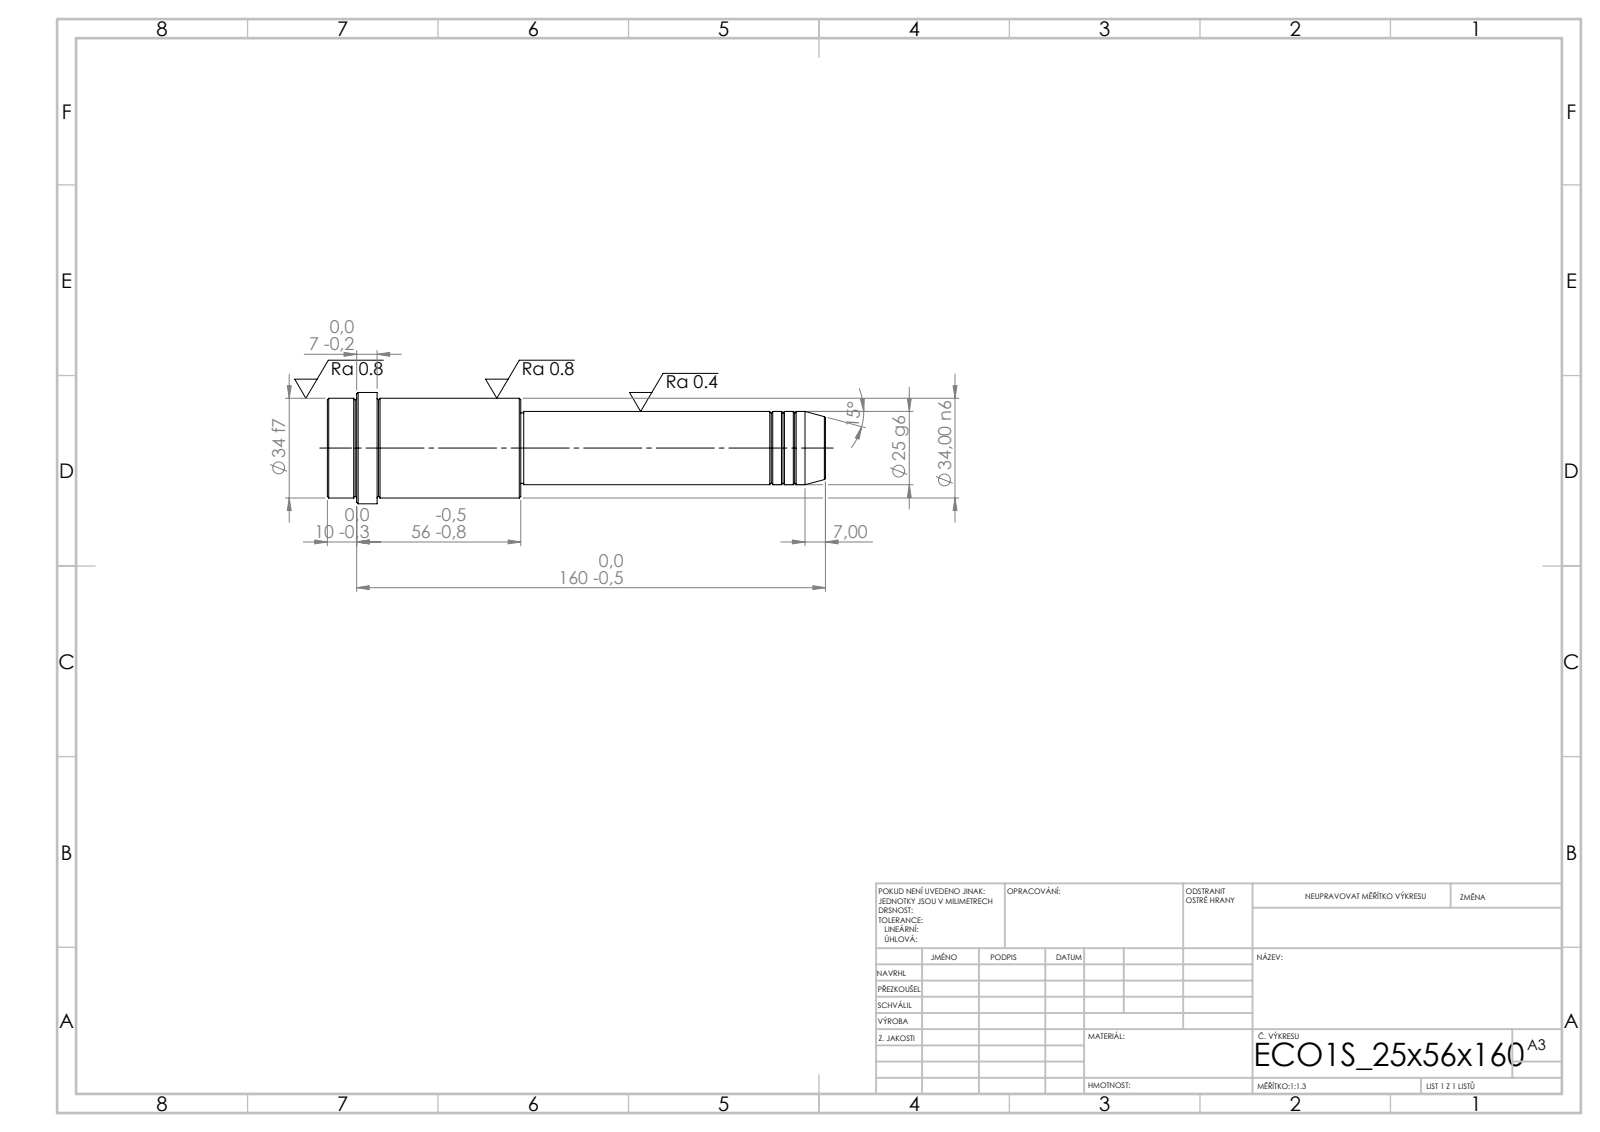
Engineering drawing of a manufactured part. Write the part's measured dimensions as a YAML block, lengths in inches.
step_written_by: "SolidWorks 2019 (CONFIG_CONTROL_DESIGN)"
units: inches
bodies: {solids: 1, faces: 52, planar: 6, cylindrical: 16, other: 30}
overall_size: [6.693, 1.496, 1.496]
volume: 6.823
surface_area: 27.32
round_bosses_or_shafts:
  - {diameter: 1.496, count: 1}
  - {diameter: 1.339, count: 1}
  - {diameter: 0.984, count: 1}
  - {diameter: 0.945, count: 1}
face_to_face_distances: [2.598, 4.094, 6.693, 6.024, 1.929, 0.669, 6.299, 2.205, 0.276, 0.394]
